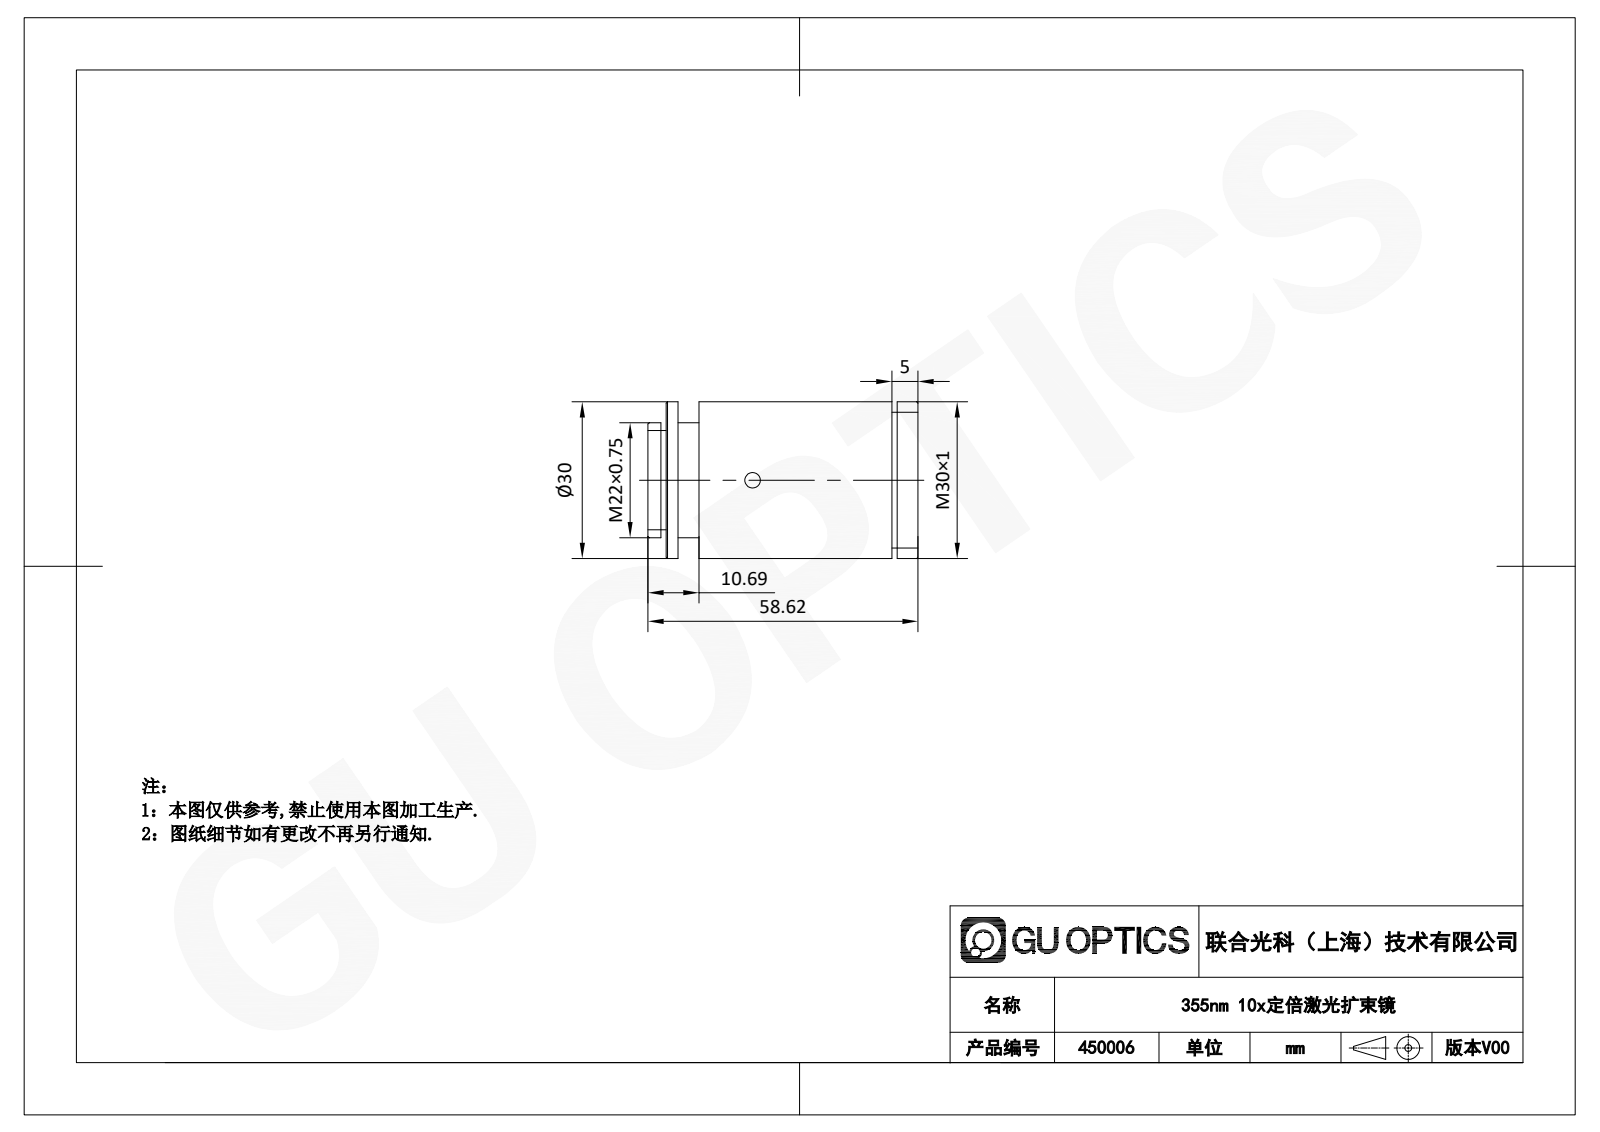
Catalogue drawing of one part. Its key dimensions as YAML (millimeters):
part_name: "450006"
step_written_by: "SolidWorks 2020 (AUTOMOTIVE_DESIGN)"
units: millimeters
bodies: {solids: 1, faces: 43, planar: 11, cylindrical: 22, other: 10}
overall_size: [58.62, 30, 30]
volume: 31536
surface_area: 10525
round_holes:
  - {diameter: 8, count: 1}
  - {diameter: 18, count: 1}
round_bosses_or_shafts:
  - {diameter: 30, count: 1}
  - {diameter: 26, count: 1}
  - {diameter: 22, count: 1}
  - {diameter: 19, count: 1}
face_to_face_distances: [4, 47.93, 51.12, 55.12, 3.19, 51.93, 7.19, 43.93, 3.5, 6.69]
